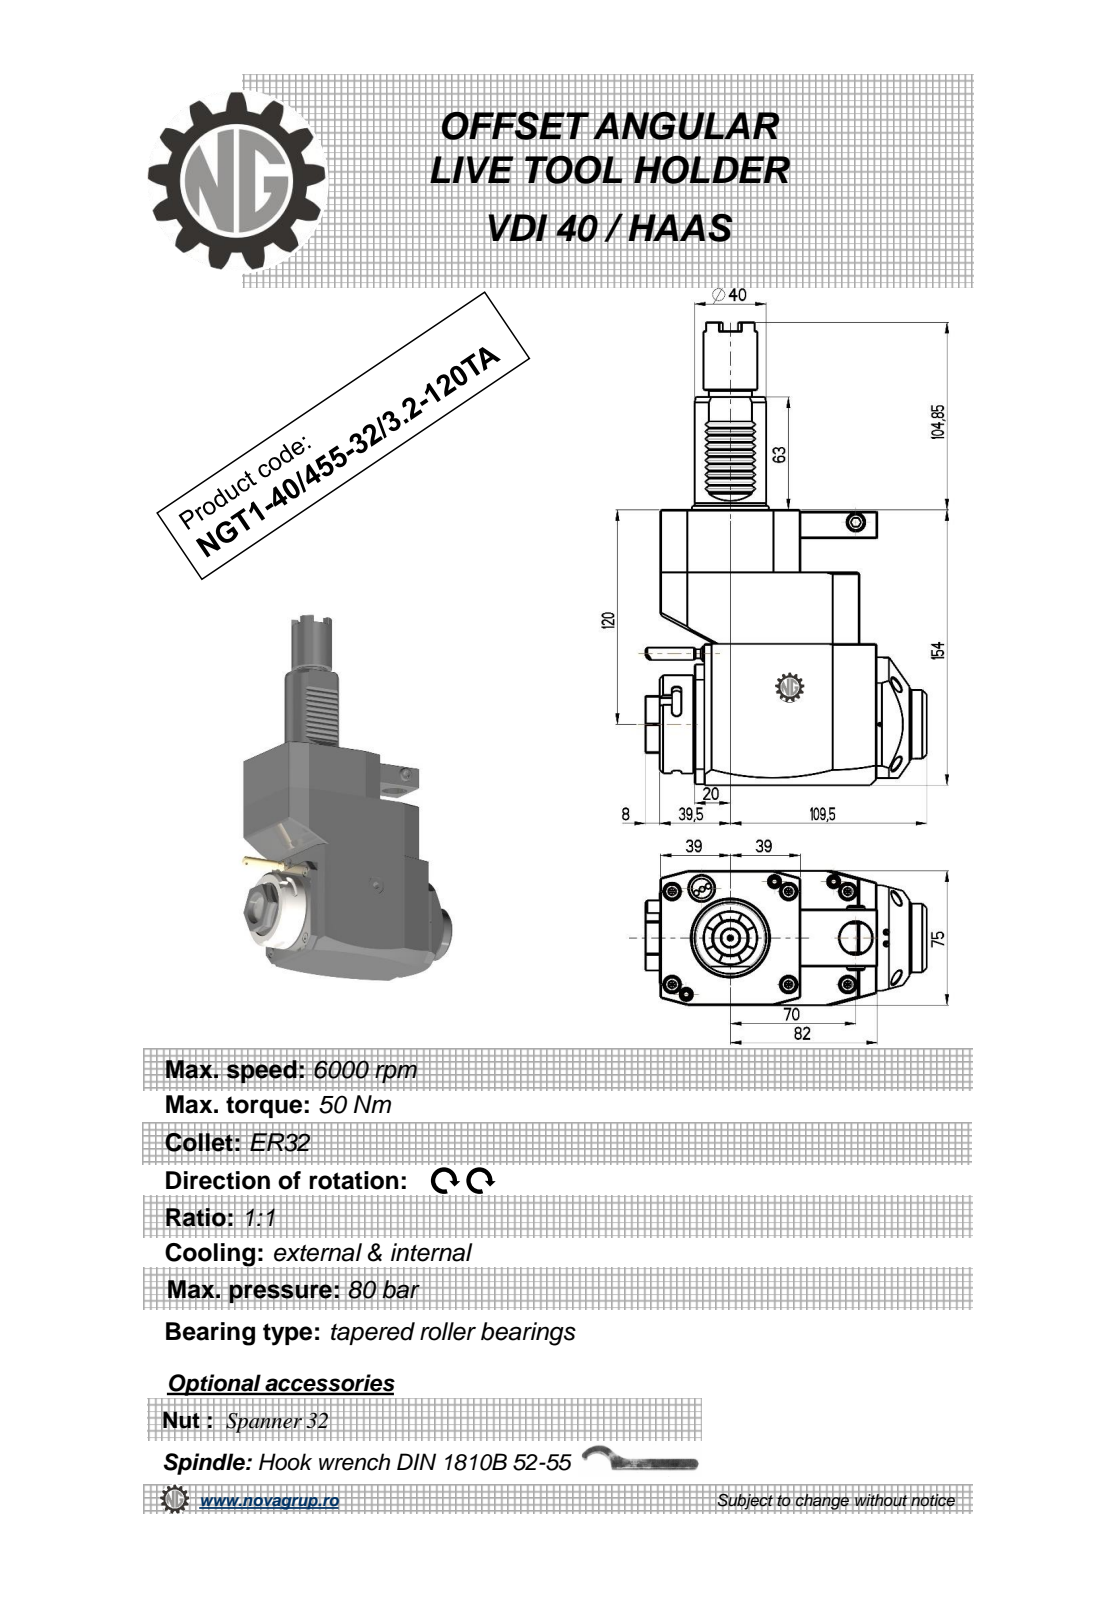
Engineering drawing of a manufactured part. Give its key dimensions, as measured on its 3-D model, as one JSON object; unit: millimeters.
{"part_name": "NGT1_40_455_32_3_2_120TA", "step_written_by": "PRO/ENGINEER BY PARAMETRIC TECHNOLOGY CORPORATION, 2010280 (CONFIG_CONTROL_DESIGN)", "units": "millimeters", "bodies": {"solids": 1, "faces": 378, "planar": 222, "cylindrical": 72, "other": 84}, "overall_size": [258.85, 157, 75], "volume_mm3": 1316000, "surface_area_mm2": 96032, "round_holes": [[2.5, 1], [3, 1], [9.5, 1], [18, 1], [23, 1]], "round_bosses_or_shafts": [[8.96, 2], [55, 1], [48, 1], [40, 1], [38.5, 1], [30, 1], [20, 1], [10, 1]], "partial_cylinders_radius": [[0.3, 10], [2.5, 6], [180, 2], [0.5, 1], [4.25, 1], [24.5, 1], [37.5, 1]], "face_to_face_distances": [75, 154, 19, 59, 0.5, 111, 33, 92, 35, 119], "hole_center_spacings": [43.2, 75.07, 112.5]}
